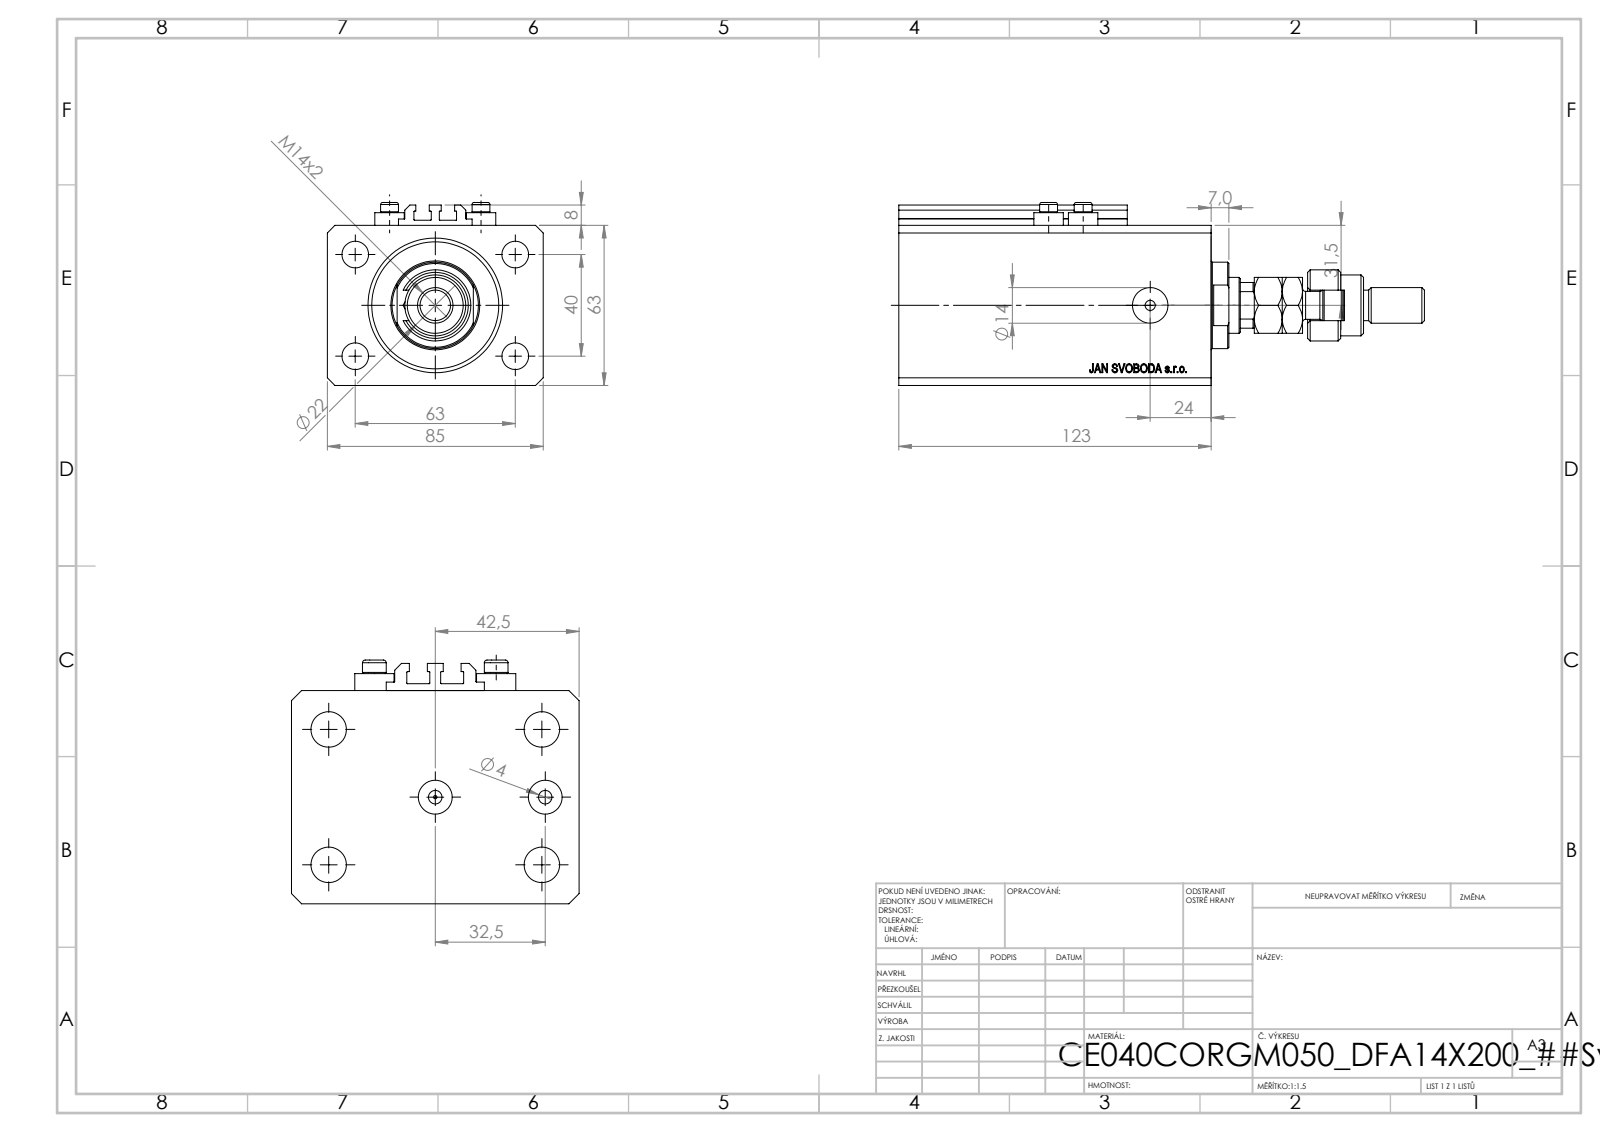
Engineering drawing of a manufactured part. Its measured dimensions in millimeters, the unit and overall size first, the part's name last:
Units: millimetres
Overall size (bounding box): 207 × 85 × 72
Round holes (diameter × count): ⌀4 ×8, ⌀10.5 ×4, ⌀10 ×2, ⌀14 ×2, ⌀1.25 ×1, ⌀12.5 ×1, ⌀22 ×1, ⌀40 ×1, ⌀53 ×1
Round bosses / shafts (diameter × count): ⌀11.6 ×4, ⌀7 ×4, ⌀34 ×1, ⌀28 ×1, ⌀24 ×1, ⌀18 ×1, ⌀14 ×1, ⌀12 ×1
Partial cylindrical surfaces — rounded edges, fillets, slot ends (radius × count): R0.2 ×10, R9.75 ×1, R10.5 ×1
Main face-to-face distances: 63, 85, 123, 17, 106, 11.4, 94.6, 111.6, 10, 2
Hole centre spacings: 37.31, 13.6, 20.02, 36, 38.48, 40, 63, 67.05
Volume: 608 772 mm³ · Surface area: 122 146 mm²
Bodies: 10 solids, 1123 faces (532 planar, 101 cylindrical, 490 other)
Part name (STEP PRODUCT): V250CE_C_Body; ALLEN BOLT V250CE; FEMALE_PART_FOR_DFA; V250CE_C_VCP (+2 more)
STEP written by: SolidWorks 2019 (CONFIG_CONTROL_DESIGN)
